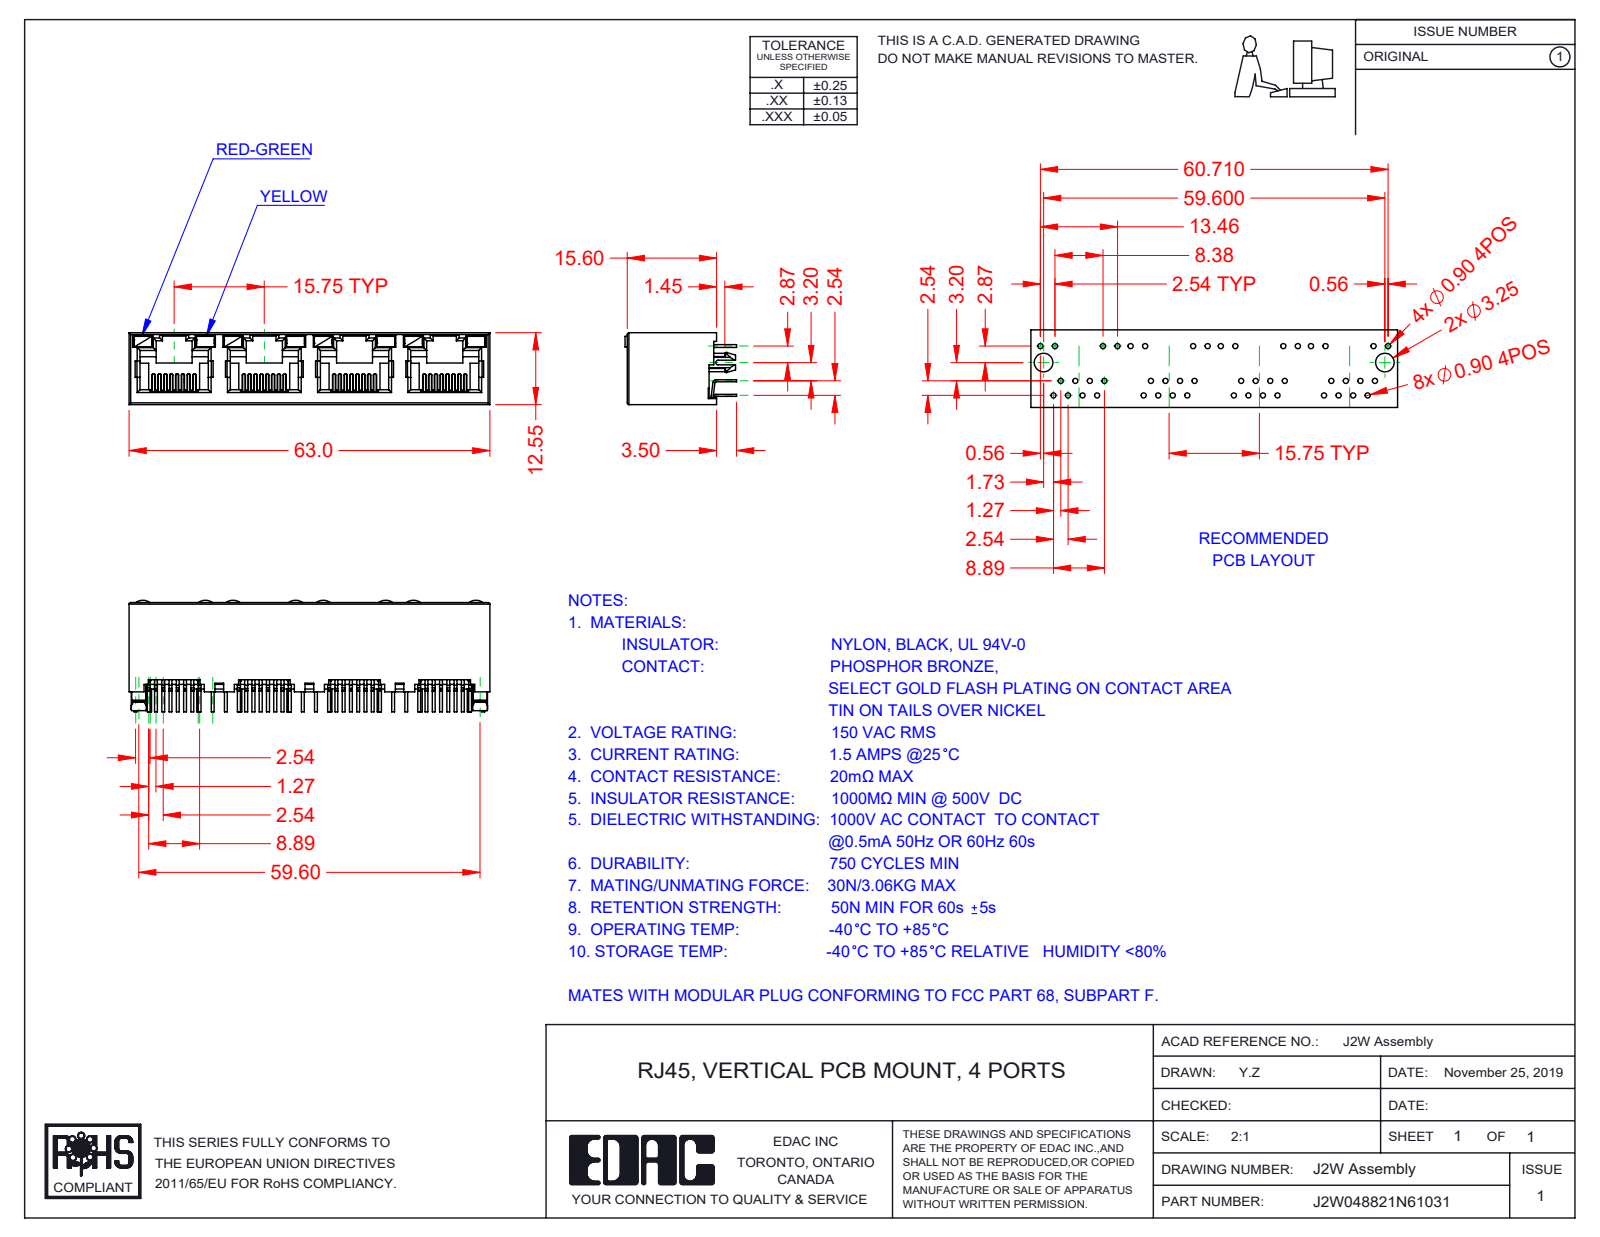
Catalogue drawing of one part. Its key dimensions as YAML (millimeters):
part_name: "2W Contact Lock; 2W LED RH_1-Yellow; 2W Insulator; J2W048821N61131 (+2 more)"
step_written_by: "SolidWorks 2016 (CONFIG_CONTROL_DESIGN)"
units: millimeters
bodies: {solids: 45, faces: 3139, planar: 2600, cylindrical: 481, other: 58}
overall_size: [63, 19.5, 12.55]
volume: 5335
surface_area: 13144
partial_cylinders:
  - {radius: 0.15, count: 64}
  - {radius: 0.2, count: 29}
  - {radius: 0.5, count: 28}
  - {radius: 0.3, count: 14}
  - {radius: 0.45, count: 8}
  - {radius: 2, count: 8}
  - {radius: 0.25, count: 2}
  - {radius: 1.5, count: 2}
face_to_face_distances: [12.55, 11.9, 0.65, 15.75, 0.36, 1.5, 0.78, 0.6, 11.3, 31.5]
